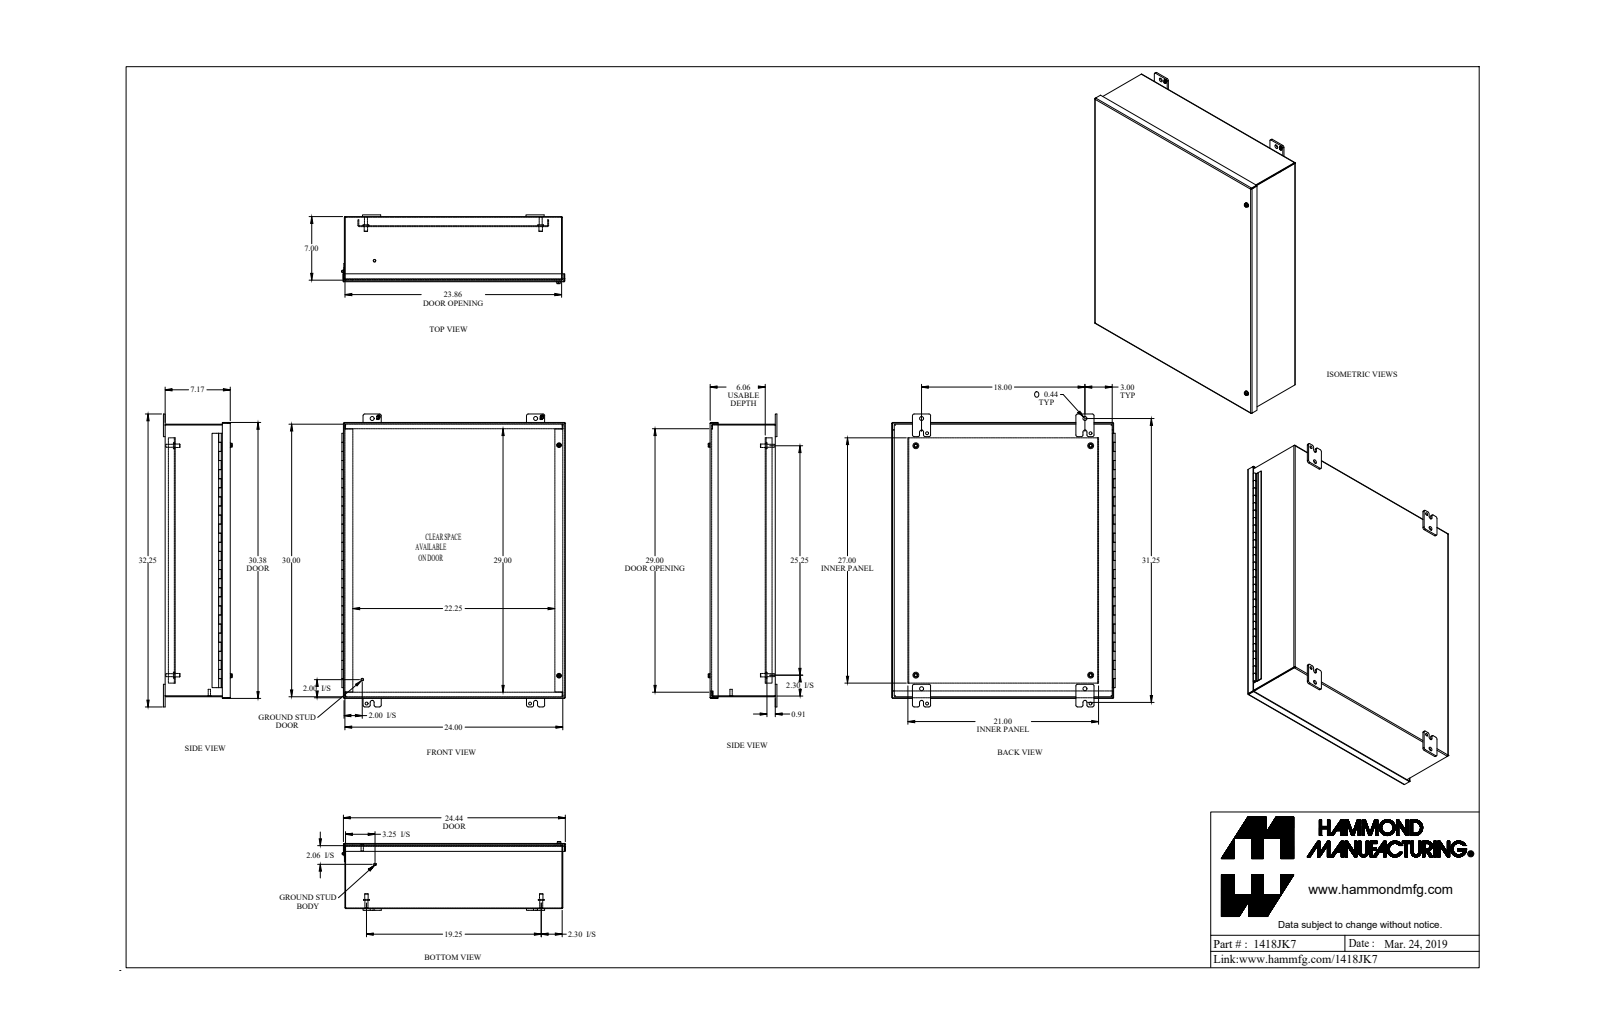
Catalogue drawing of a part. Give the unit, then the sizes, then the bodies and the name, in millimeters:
Units: millimetres
Overall size (bounding box): 819.2 × 624.9 × 192.3
Round holes (diameter × count): ⌀8 ×6, ⌀11.1 ×4, ⌀12.7 ×4, ⌀6.6 ×2, ⌀6.8 ×2, ⌀7.1 ×2, ⌀7.4 ×2, ⌀7.8 ×2, ⌀10.1 ×2, ⌀4.7 ×1, ⌀11.3 ×1, ⌀11.3 ×1
Round bosses / shafts (diameter × count): ⌀16.5 ×4, ⌀9.5 ×4, ⌀8.4 ×4, ⌀25.4 ×2, ⌀13 ×2, ⌀12.7 ×2, ⌀9.9 ×2, ⌀7.1 ×2
Partial cylindrical surfaces — rounded edges, fillets, slot ends (radius × count): R4.8 ×24, R6.4 ×20, R0.9 ×12, R2.7 ×12, R5.5 ×8, R3.4 ×6, R1.5 ×5, R3.2 ×4
Main face-to-face distances: 1.8, 180.3, 182.2, 178.5, 2.4, 152.3, 154.7, 28, 26.2, 154.1
Hole centre spacings: 806.5, 44.1, 457.2, 489, 755.7, 838.9, 883.2, 48.4
Volume: 4 325 000 mm³ · Surface area: 4 198 000 mm²
Bodies: 32 solids, 978 faces (599 planar, 337 cylindrical, 42 other)
Part name (STEP PRODUCT): 1418JK7_Default
STEP written by: SolidWorks 2018 (CONFIG_CONTROL_DESIGN)
